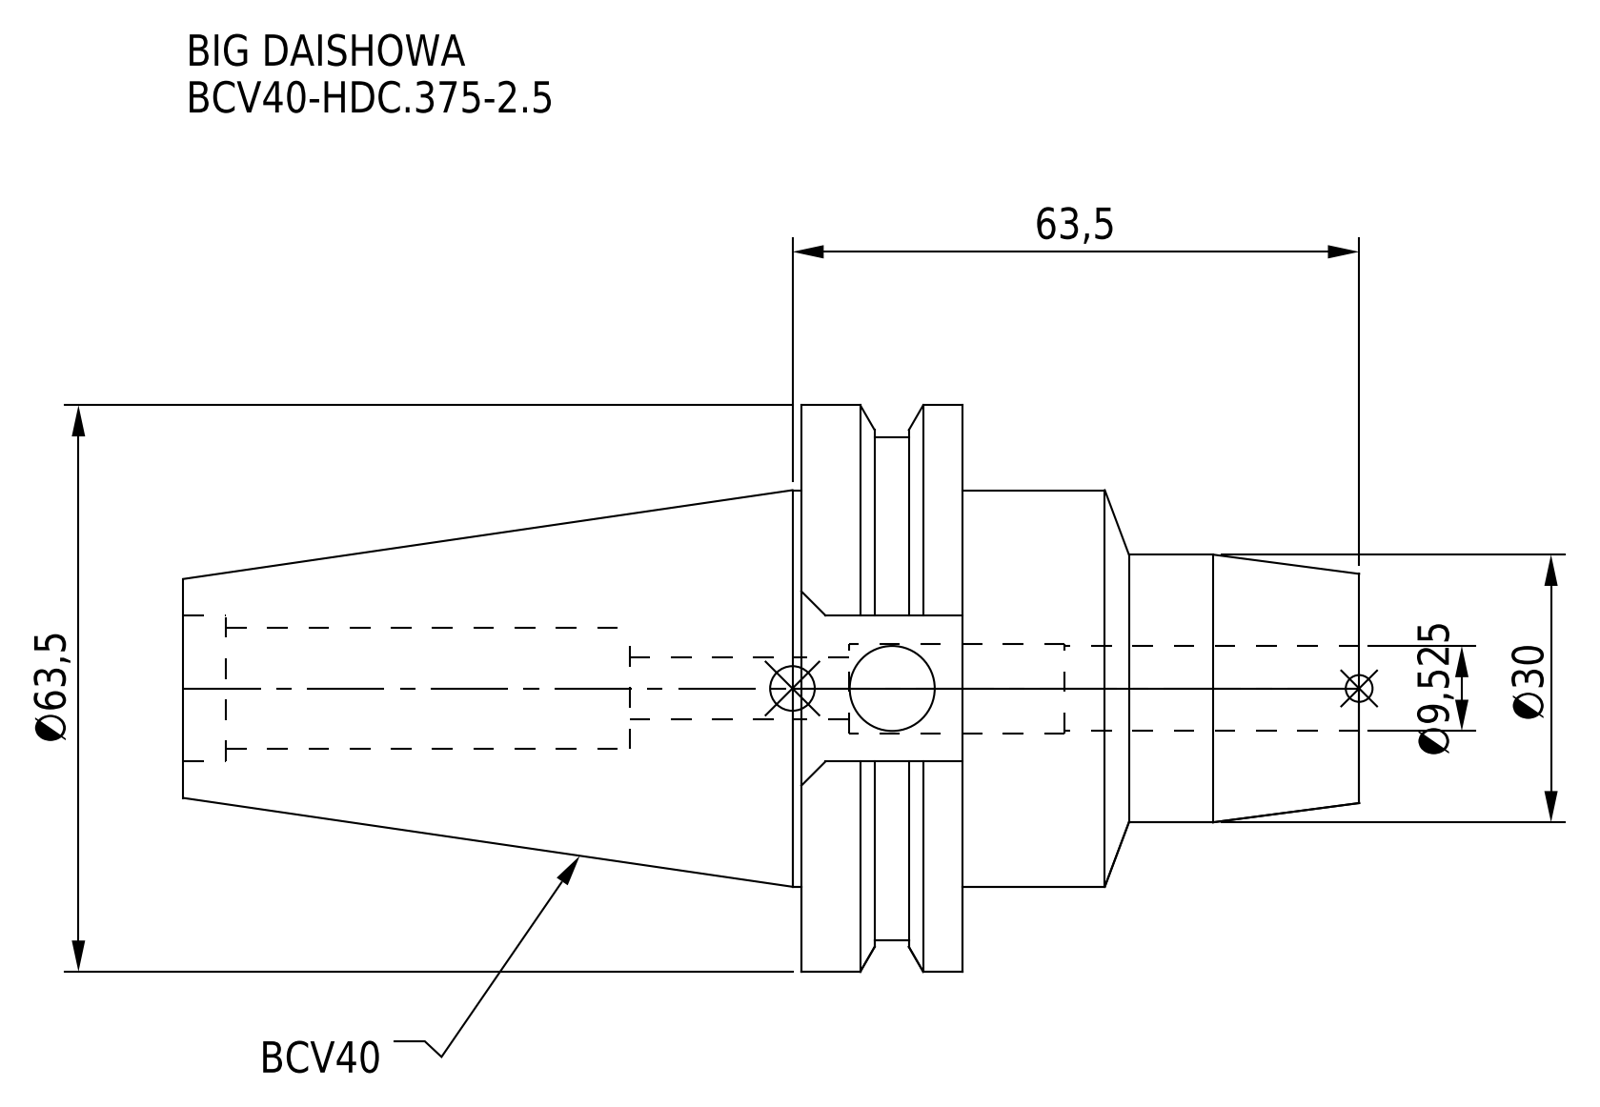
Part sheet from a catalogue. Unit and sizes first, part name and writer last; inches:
Units: inches
Overall size (bounding box): 5.187 × 2.5 × 2.415
Round holes (diameter × count): ⌀0.375 ×2, ⌀0.276 ×1, ⌀0.394 ×1, ⌀0.535 ×1, ⌀0.643 ×1
Round bosses / shafts (diameter × count): ⌀2.5 ×1, ⌀2.219 ×1, ⌀1.75 ×1, ⌀1.181 ×1
Main face-to-face distances: 0.711, 1.75, 2.461, 5.187, 3.437, 2.726, 1.872, 0.645, 2.137, 0.387
Volume: 9.057 in³ · Surface area: 40 in²
Bodies: 1 solid, 59 faces (23 planar, 26 cylindrical, 10 other)
Part name (STEP PRODUCT): BCV40-HDC_375-2_5
STEP written by: CREO PARAMETRIC BY PTC INC, 2016380 (AUTOMOTIVE_DESIGN)
